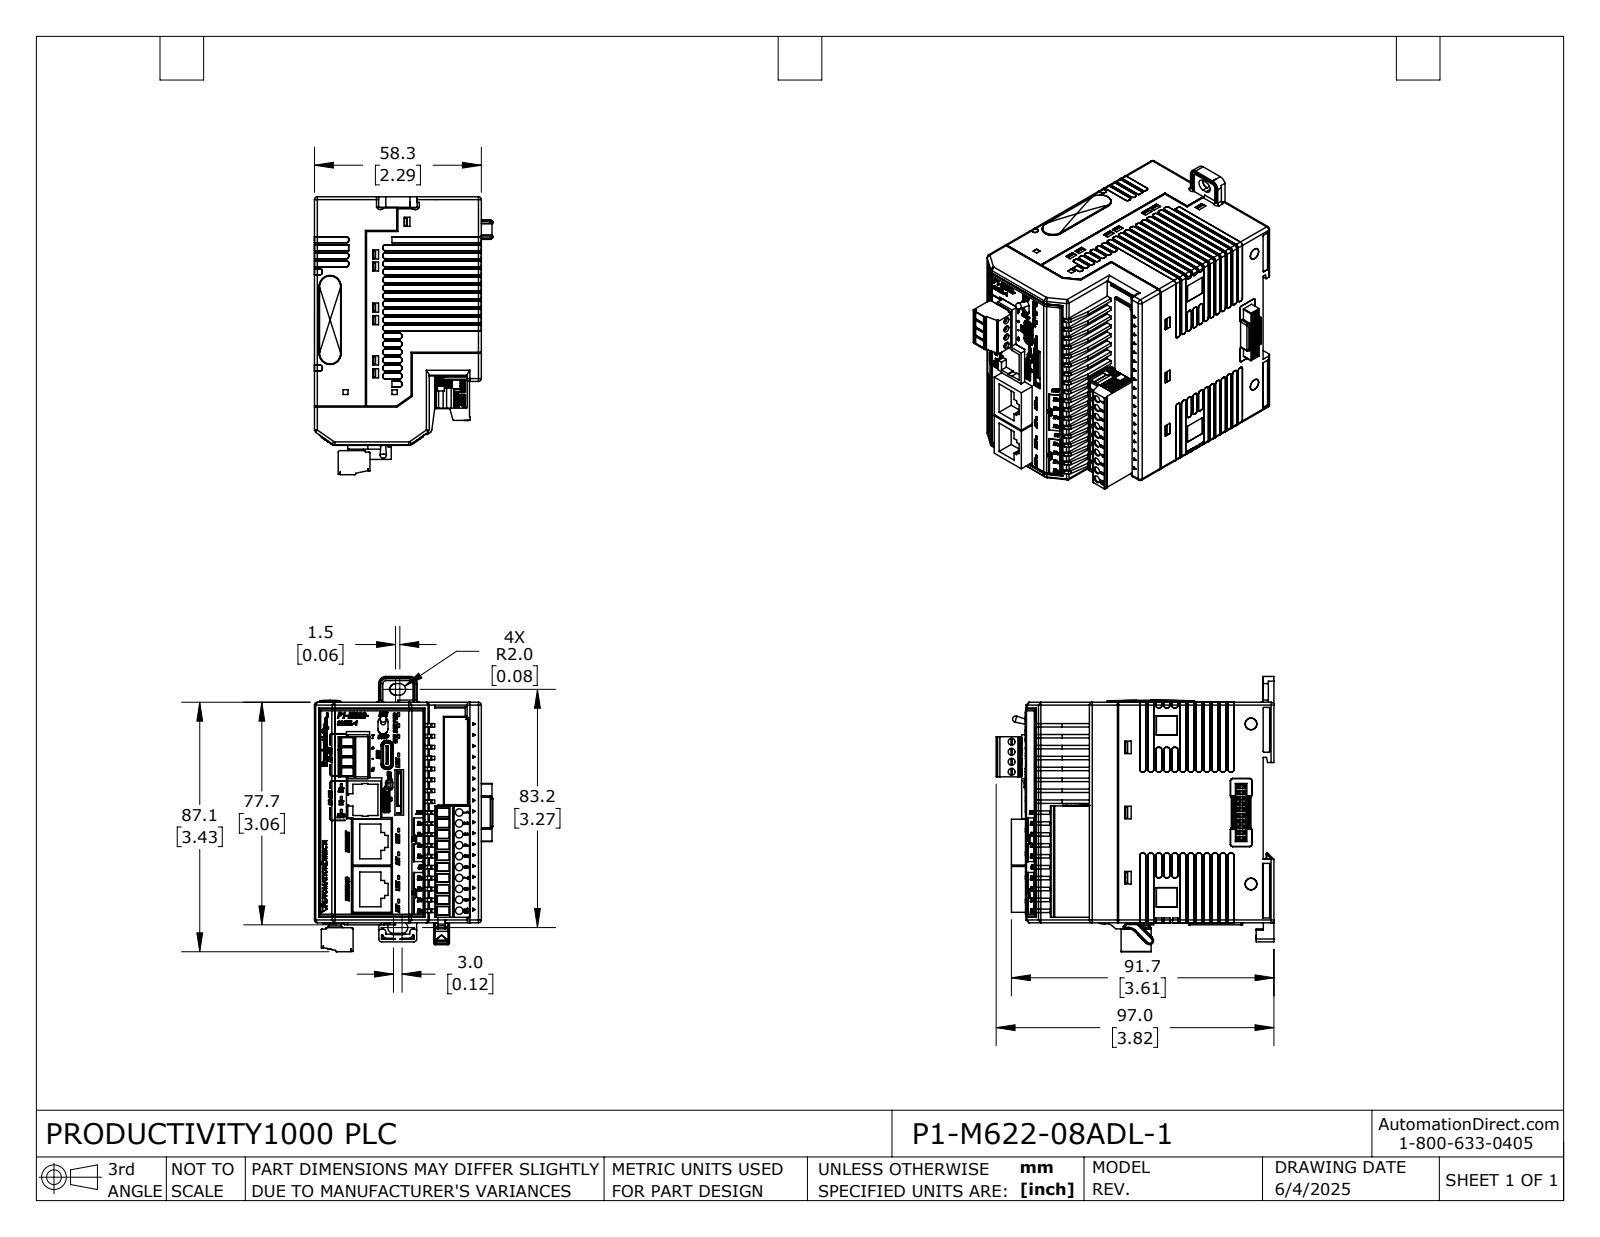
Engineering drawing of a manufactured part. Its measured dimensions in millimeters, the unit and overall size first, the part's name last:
Units: millimetres
Overall size (bounding box): 93.6 × 91.7 × 62.3
Partial cylindrical surfaces — rounded edges, fillets, slot ends (radius × count): R0.3 ×186, R0.2 ×80, R0.5 ×53, R1 ×33, R2 ×8, R0.6 ×7, R1.5 ×7, R0.3 ×4
Main face-to-face distances: 1.3, 0.5, 56.8, 1, 57.8, 76.5, 76.8, 58.3, 76.7, 77
Volume: 35 820 mm³ · Surface area: 77 420 mm²
Bodies: 15 solids, 3822 faces (2189 planar, 892 cylindrical, 741 other)
Part name (STEP PRODUCT): P1-M622-08ADL-1
STEP written by: SolidWorks 2024 (AUTOMOTIVE_DESIGN)
